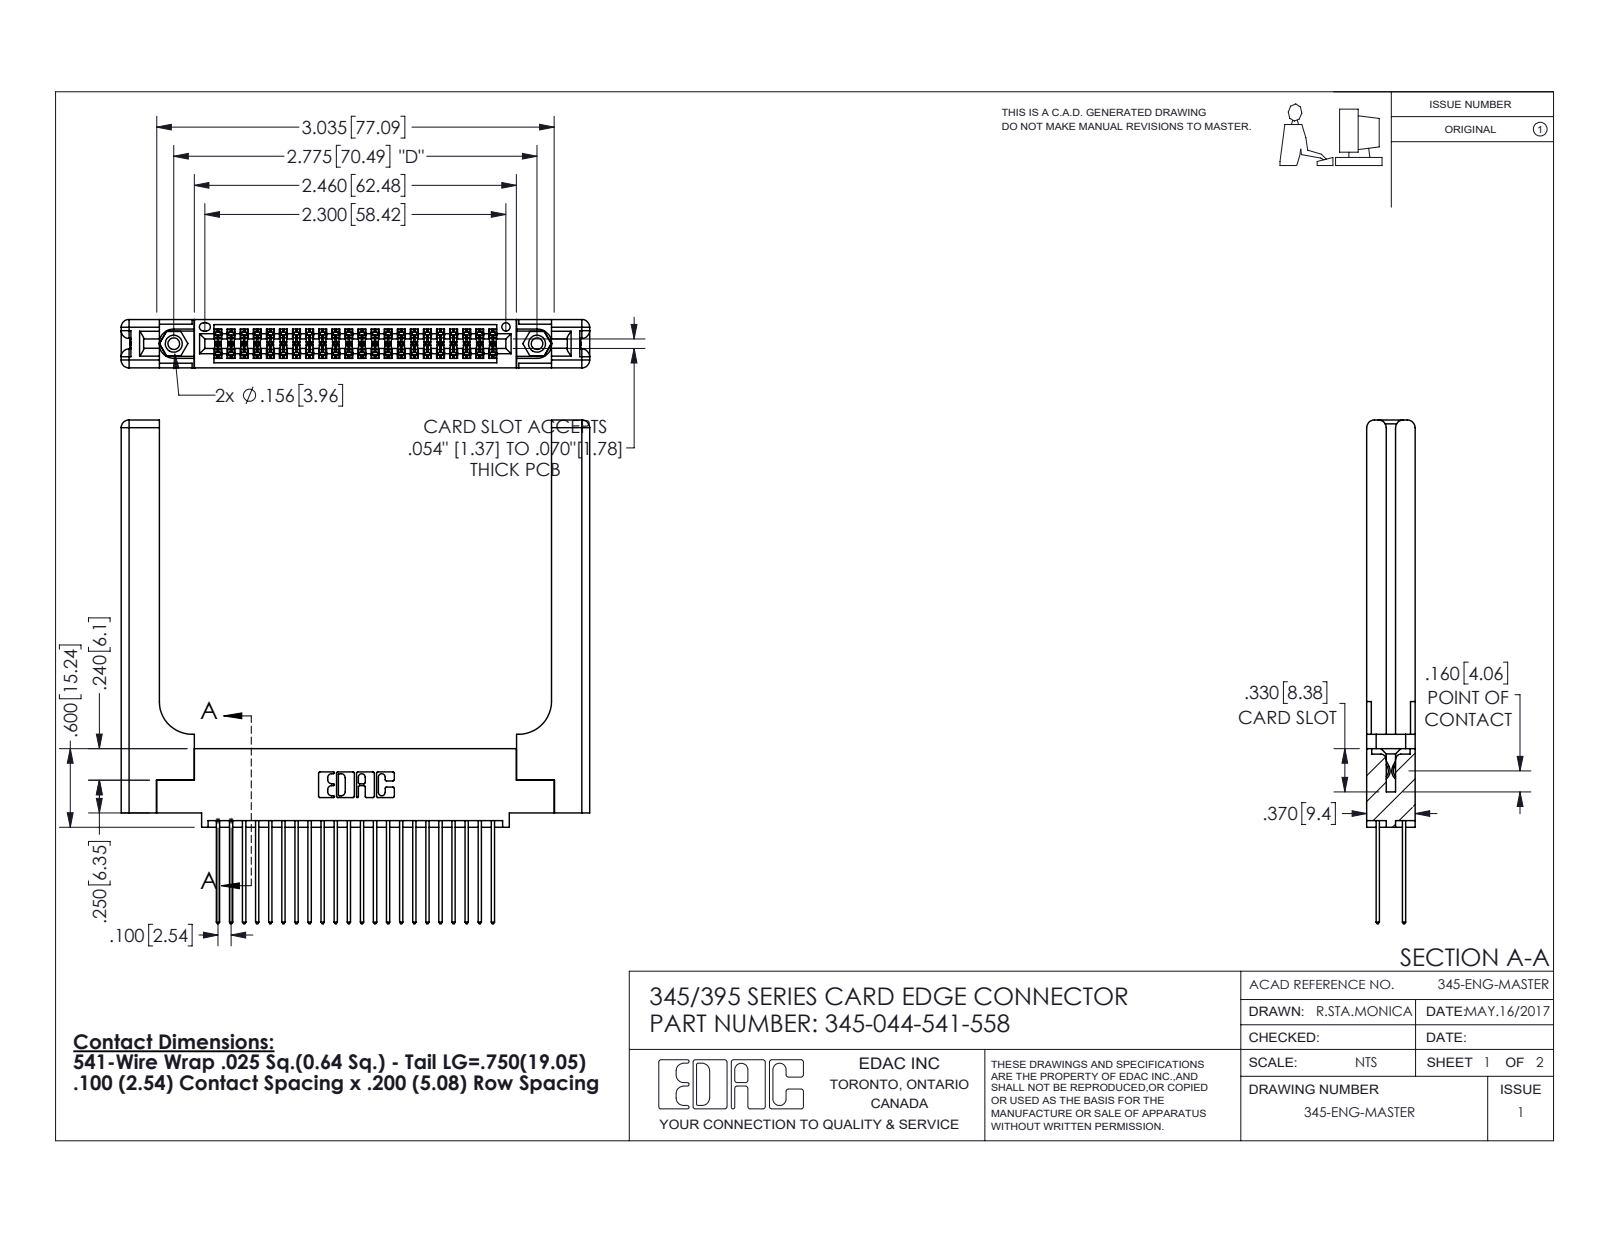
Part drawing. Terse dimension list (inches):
name: 345-250-001_345-250-001-102; 345-044-541-558; 345-292-001_345-293-141; 345 Part_0.110 Offset - 0.156 Dia-TH (+1 more)
written by: SolidWorks 2016 (CONFIG_CONTROL_DESIGN)
unit: in
bodies: 49 solids, 2586 faces (1684 planar, 842 cylindrical, 60 other)
size: 3.847 × 3.579 × 0.37
volume: 1.056 in³; area: 29.44 in²
holes: 2× ⌀0.089, 2× ⌀0.125, 2× ⌀0.156, 1× ⌀0.064
bosses: 2× ⌀0.155
rounds: 66× R0.006, 44× R0.01, 22× R0.01, 16× R0.06, 6× R0.007, 6× R0.031, 3× R0.026, 2× R0.014
face distances: 0.072, 0.37, 0.298, 0.098, 0.272, 0.025, 0.2, 0.225, 0.15, 0.148
hole spacings: 0.27, 2.541, 2.775
